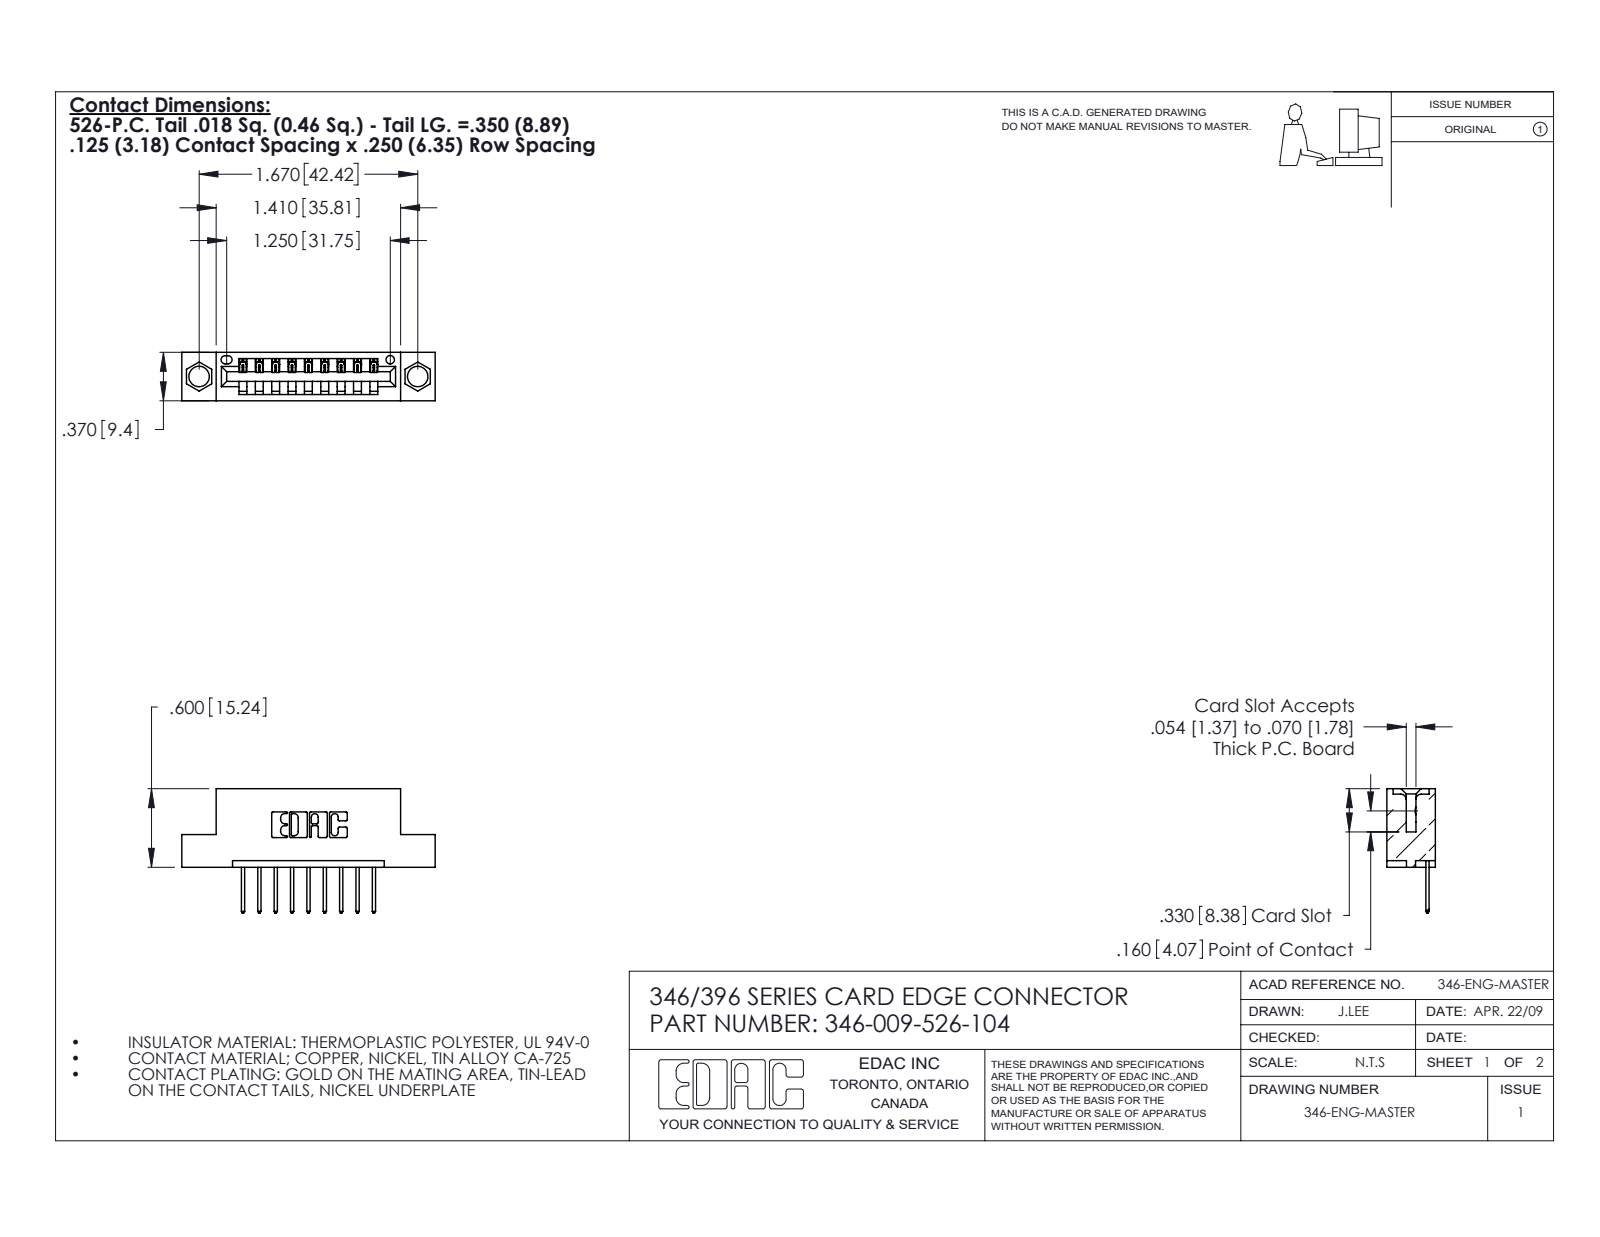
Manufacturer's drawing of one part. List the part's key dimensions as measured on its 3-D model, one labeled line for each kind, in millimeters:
Part name (STEP PRODUCT): 346 Part_Flush Mounting Lugs - 0.156 Dia-TH; 345-292-001_345-293-126; 346-009-526-104
STEP written by: SolidWorks 2020 (CONFIG_CONTROL_DESIGN)
Units: millimetres
Bodies: 10 solids, 658 faces (450 planar, 208 cylindrical, 0 other)
Overall size (bounding box): 49.1 × 24.1 × 9.4
Volume: 4 360 mm³ · Surface area: 4 927 mm²
Round holes (diameter × count): ⌀4 ×2, ⌀1.6 ×1
Partial cylindrical surfaces — rounded edges, fillets, slot ends (radius × count): R0.3 ×22, R0.2 ×18, R0.3 ×18, R0.2 ×6, R0.8 ×6, R0.7 ×3, R0.8 ×2, R1 ×2
Main face-to-face distances: 6.4, 9.4, 1.2, 8.2, 1.8, 7.6, 0.6, 3.8, 5.6, 2.5
Hole centre spacings: 6.2, 37.2, 42.4
